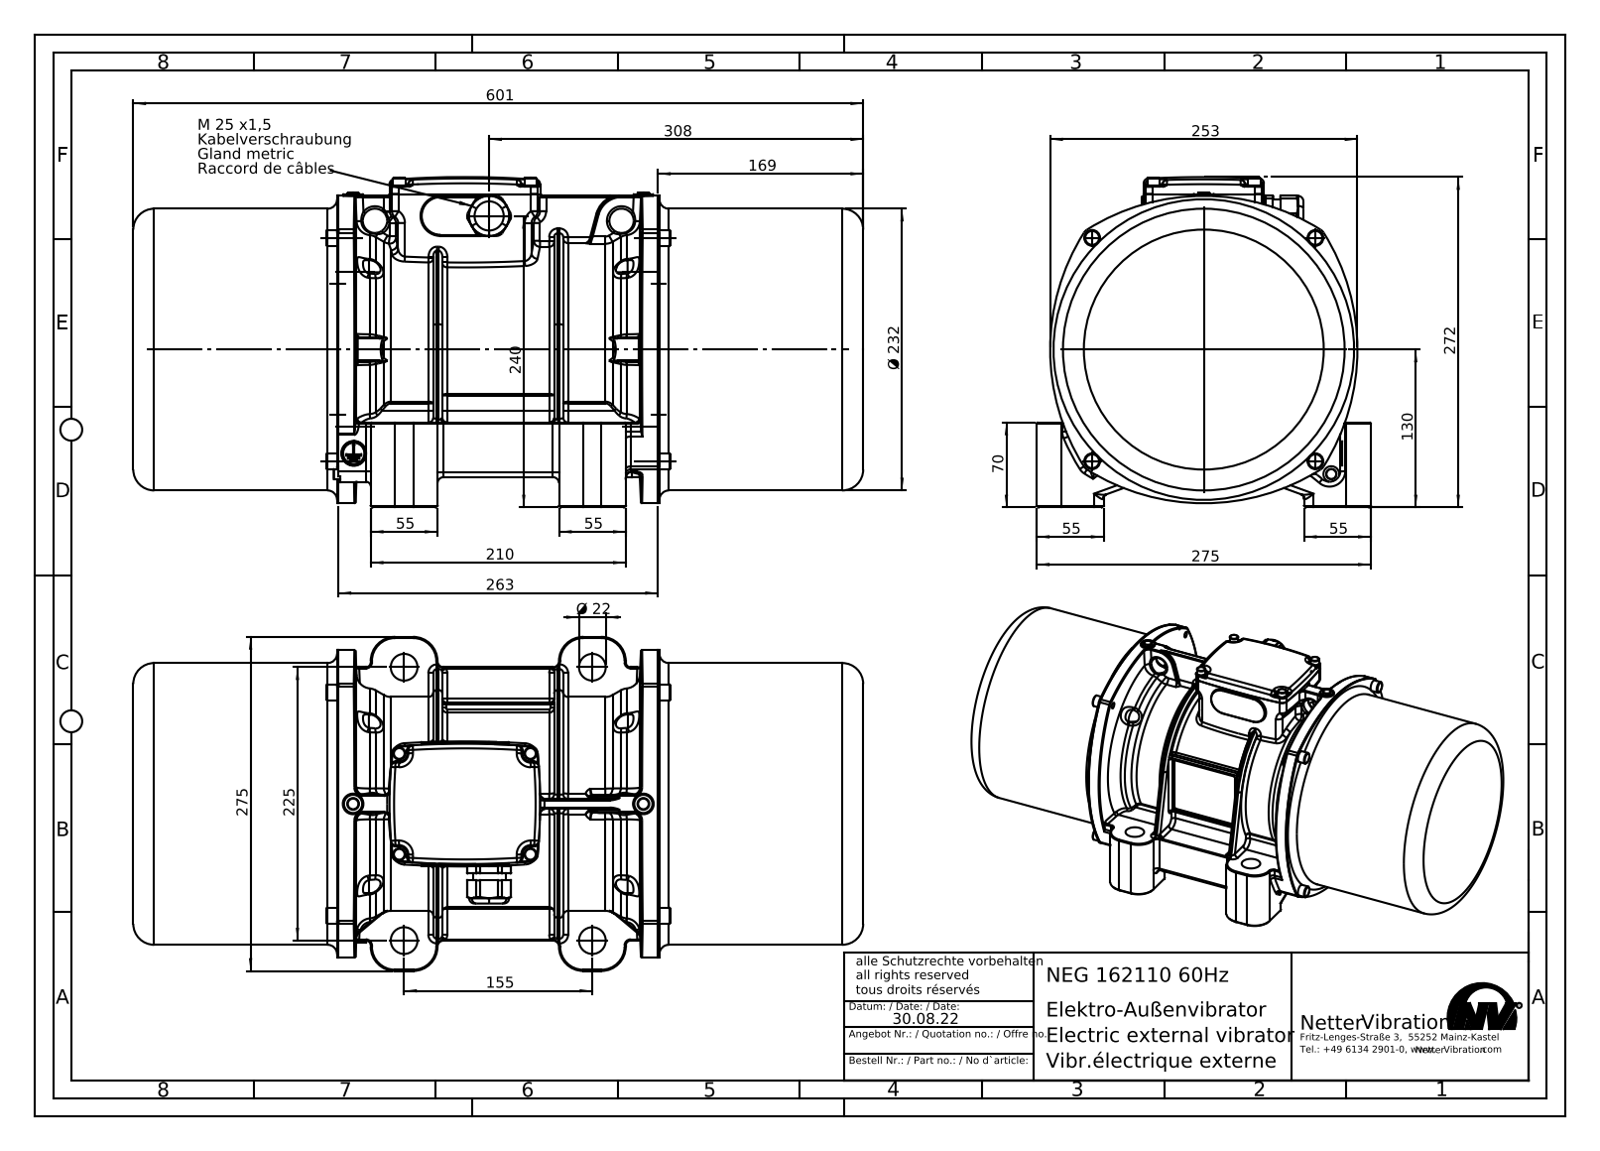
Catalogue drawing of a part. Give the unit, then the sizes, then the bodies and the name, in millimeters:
Units: millimetres
Overall size (bounding box): 601 × 275 × 272
Round holes (diameter × count): ⌀22 ×4, ⌀20 ×2, ⌀13 ×1, ⌀18 ×1, ⌀25 ×1, ⌀152 ×1, ⌀210 ×1, ⌀243 ×1
Round bosses / shafts (diameter × count): ⌀10 ×8, ⌀16 ×4, ⌀13 ×4, ⌀8 ×4, ⌀6 ×4, ⌀9.73 ×2, ⌀231.9 ×1, ⌀165 ×1
Partial cylindrical surfaces — rounded edges, fillets, slot ends (radius × count): R0.2 ×102, R4 ×57, R5 ×56, R1 ×24, R3 ×20, R8 ×17, R2 ×14, R10 ×10
Main face-to-face distances: 172.5, 428.5, 3.5, 169, 432, 259.5, 241.5, 190.5, 18, 410.5
Hole centre spacings: 136.61, 155, 225, 273.22, 20.16, 116.92, 134.78, 141.32
Volume: 22 940 000 mm³ · Surface area: 1 327 000 mm²
Bodies: 14 solids, 2851 faces (509 planar, 632 cylindrical, 1710 other)
Part name (STEP PRODUCT): 602426C NEG 162110 60HZ
STEP written by: SolidWorks 2015 (AUTOMOTIVE_DESIGN)
